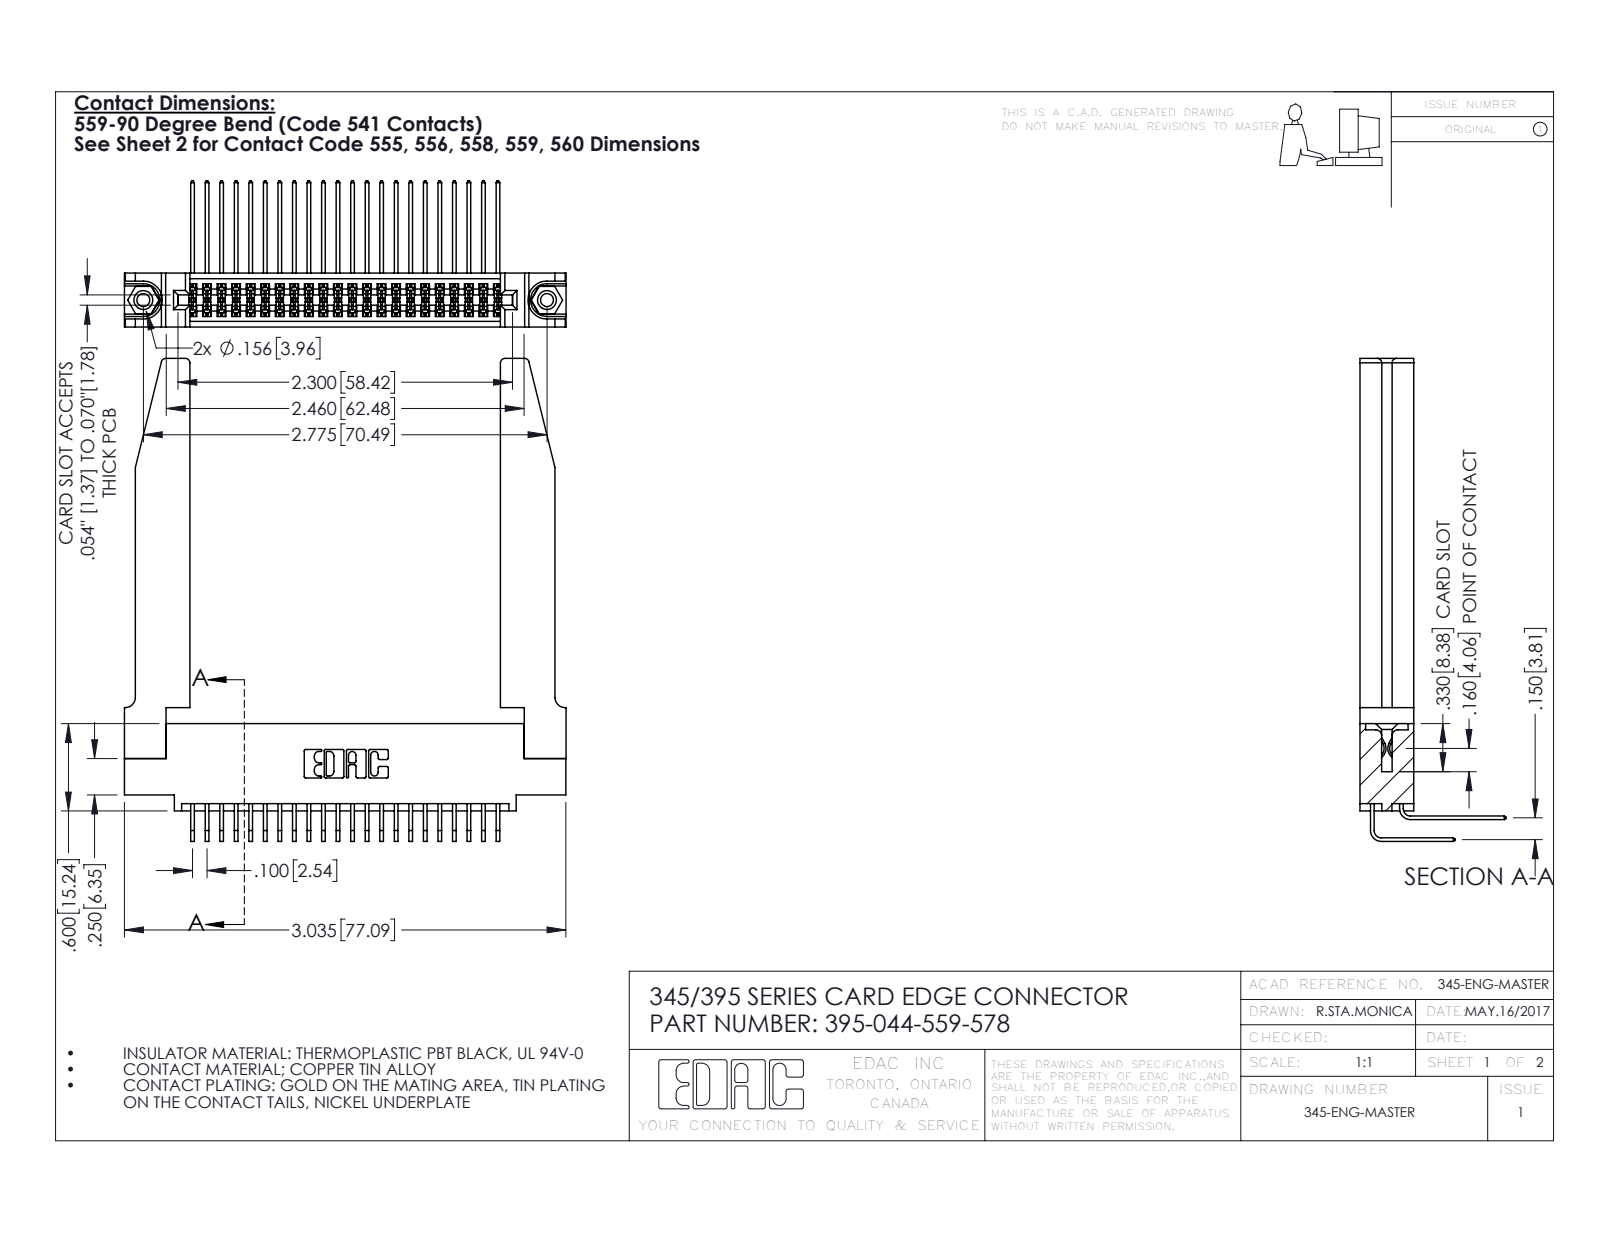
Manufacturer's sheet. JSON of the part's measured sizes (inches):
{"part_name": "395-044-559-578; 345 Part_0.110 Offset - 0.156 Dia-TH; 345-220-078_345-220-078; 345-250-001_345-250-001-102 (+2 more)", "step_written_by": "SolidWorks 2016 (CONFIG_CONTROL_DESIGN)", "units": "inches", "bodies": {"solids": 49, "faces": 2652, "planar": 1766, "cylindrical": 834, "other": 52}, "overall_size": [3.319, 3.036, 1.005], "volume_in3": 0.931, "surface_area_in2": 29.14, "round_holes": [[0.089, 2], [0.125, 2], [0.156, 2], [0.064, 1]], "round_bosses_or_shafts": [[0.155, 2]], "partial_cylinders_radius": [[0.006, 67], [0.01, 22], [0.03, 8], [0.007, 6], [0.031, 6], [0.026, 3], [0.014, 2], [0.019, 2]], "face_to_face_distances": [0.37, 0.072, 0.298, 0.2, 0.098, 0.272, 0.025, 0.225, 0.148, 0.15], "hole_center_spacings": [0.27, 2.541, 2.775]}
